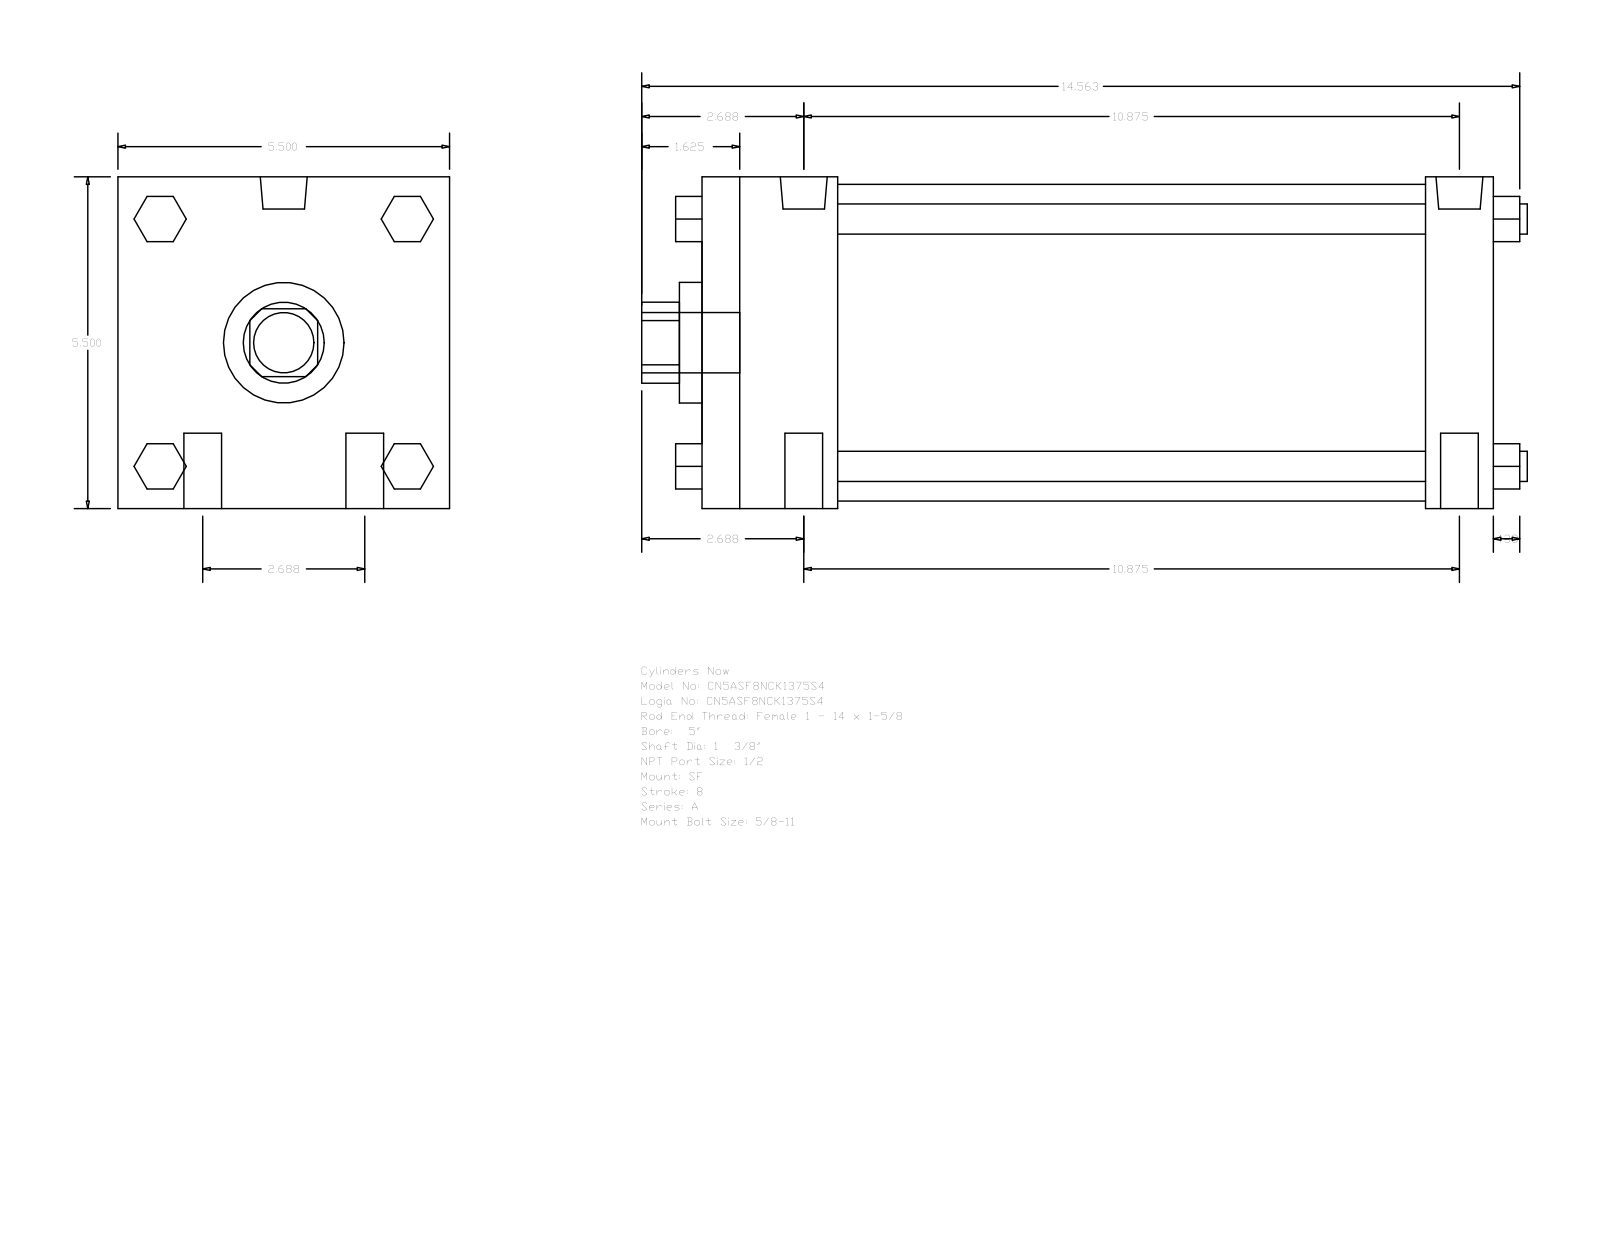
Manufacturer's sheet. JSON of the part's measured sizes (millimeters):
{"part_name": "A_SF__0500_1.375", "step_written_by": "GSSL Pune (CONFIG_CONTROL_DESIGN)", "units": "millimeters", "bodies": {"solids": 0, "faces": 124, "planar": 94, "cylindrical": 30, "other": 0}, "overall_size": [373.06, 139.7, 139.7], "round_holes": [[34.92, 1], [50.8, 1], [133.35, 1]], "round_bosses_or_shafts": [[15.88, 4], [12.7, 4], [19.77, 2], [8.73, 2], [25.4, 1]], "partial_cylinders_radius": [[17.06, 1]], "face_to_face_distances": [139.7, 333.37, 28.57, 57.15, 304.8, 247.65, 276.22, 19.05, 52.07, 90.18]}
